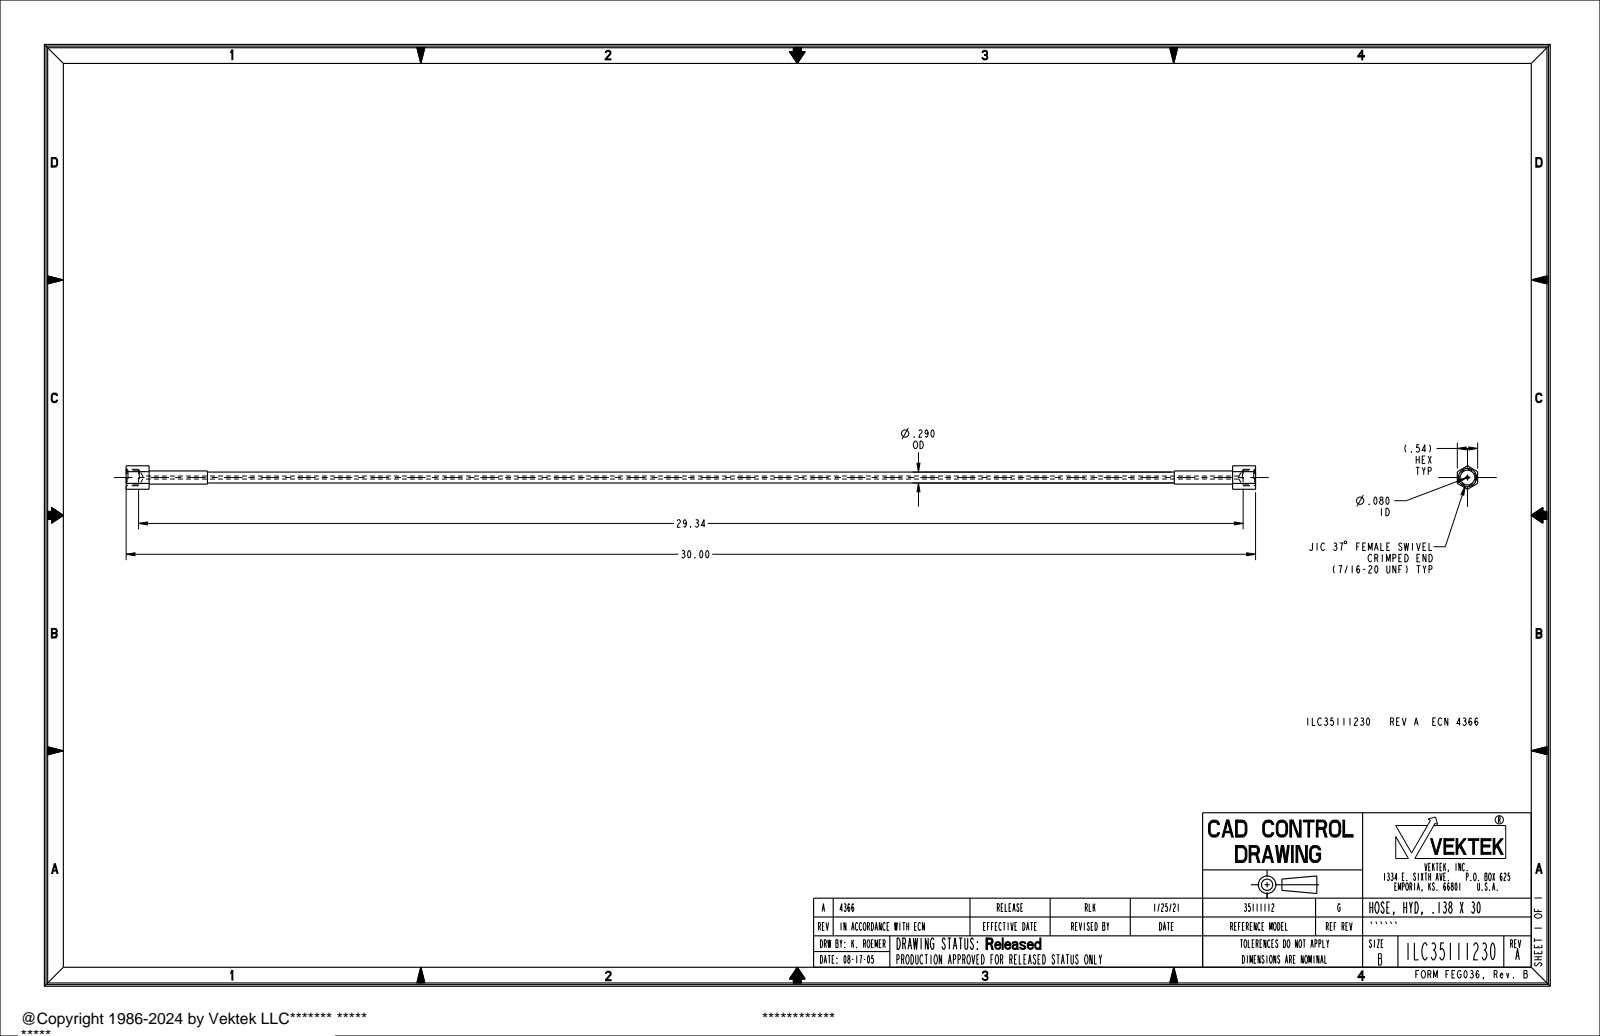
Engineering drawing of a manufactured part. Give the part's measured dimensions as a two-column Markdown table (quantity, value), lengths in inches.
| quantity | value |
| --- | --- |
| part name | ILC35111230 |
| STEP written by | PRO/ENGINEER BY PARAMETRIC TECHNOLOGY CORPORATION, 2017170 (AUTOMOTIVE_DESIGN) |
| units | inches |
| bodies | 1 solid, 44 faces (20 planar, 16 cylindrical, 8 other) |
| overall size | 30 × 0.624 × 0.54 |
| volume | 2.06 in³ |
| surface area | 39 in² |
| round holes (diameter × count) | 0.08 × 1, 0.391 × 1, 0.437 × 1 |
| round bosses / shafts (diameter × count) | 0.35 × 1, 0.29 × 1 |
| main face-to-face distances | 0.54, 28.78, 0.61, 29.39, 30, 0.33, 29.67, 0.28, 29.06, 2.16 |
